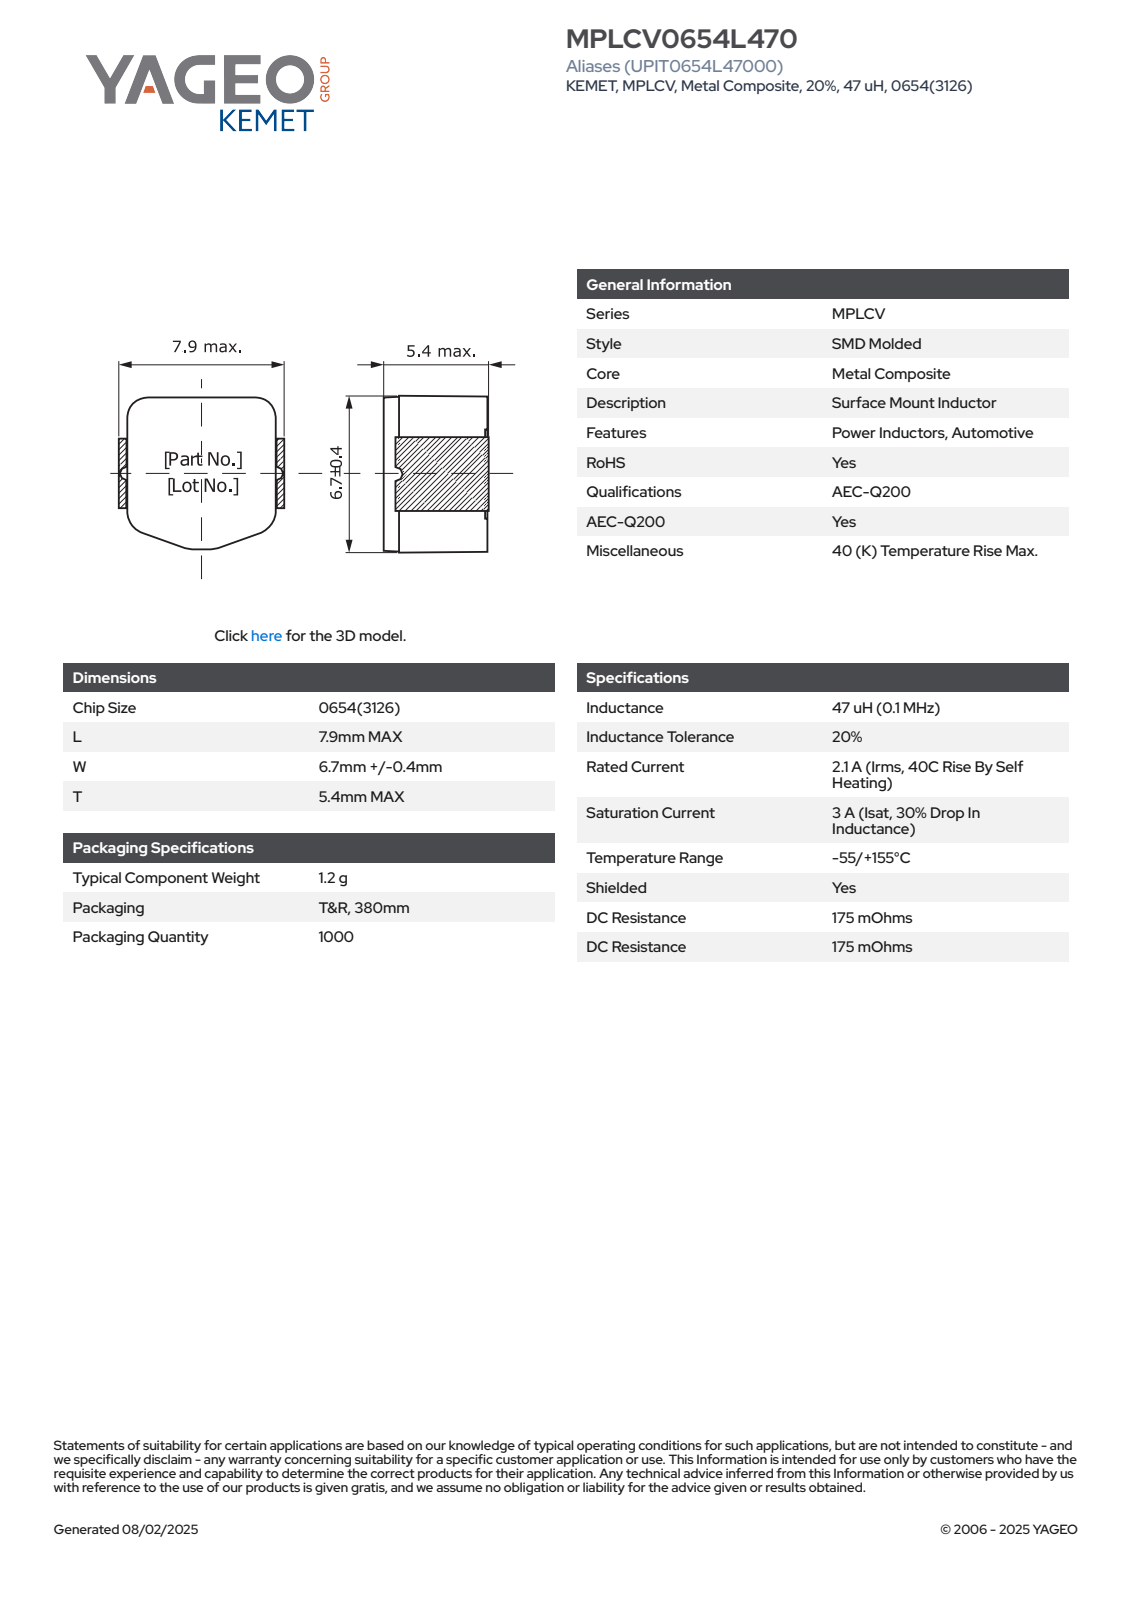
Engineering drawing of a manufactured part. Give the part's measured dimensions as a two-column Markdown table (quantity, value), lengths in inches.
| quantity | value |
| --- | --- |
| part name | IS_MPLCV_0654(3126)_L7.9W7.1T5.4 |
| STEP written by | SolidWorks 2014 (AUTOMOTIVE_DESIGN) |
| units | inches |
| bodies | 4 solids, 116 faces (95 planar, 21 cylindrical, 0 other) |
| overall size | 0.311 × 0.28 × 0.213 |
| volume | 0.016 in³ |
| surface area | 0.445 in² |
| partial cylindrical surfaces (radius × count) | 0.039 × 4, 0.024 × 2, 0.006 × 1 |
| main face-to-face distances | 0.213, 0.303, 0.295, 0.307, 0.299, 0.209, 0.311, 0.28, 0.113, 0.118 |
